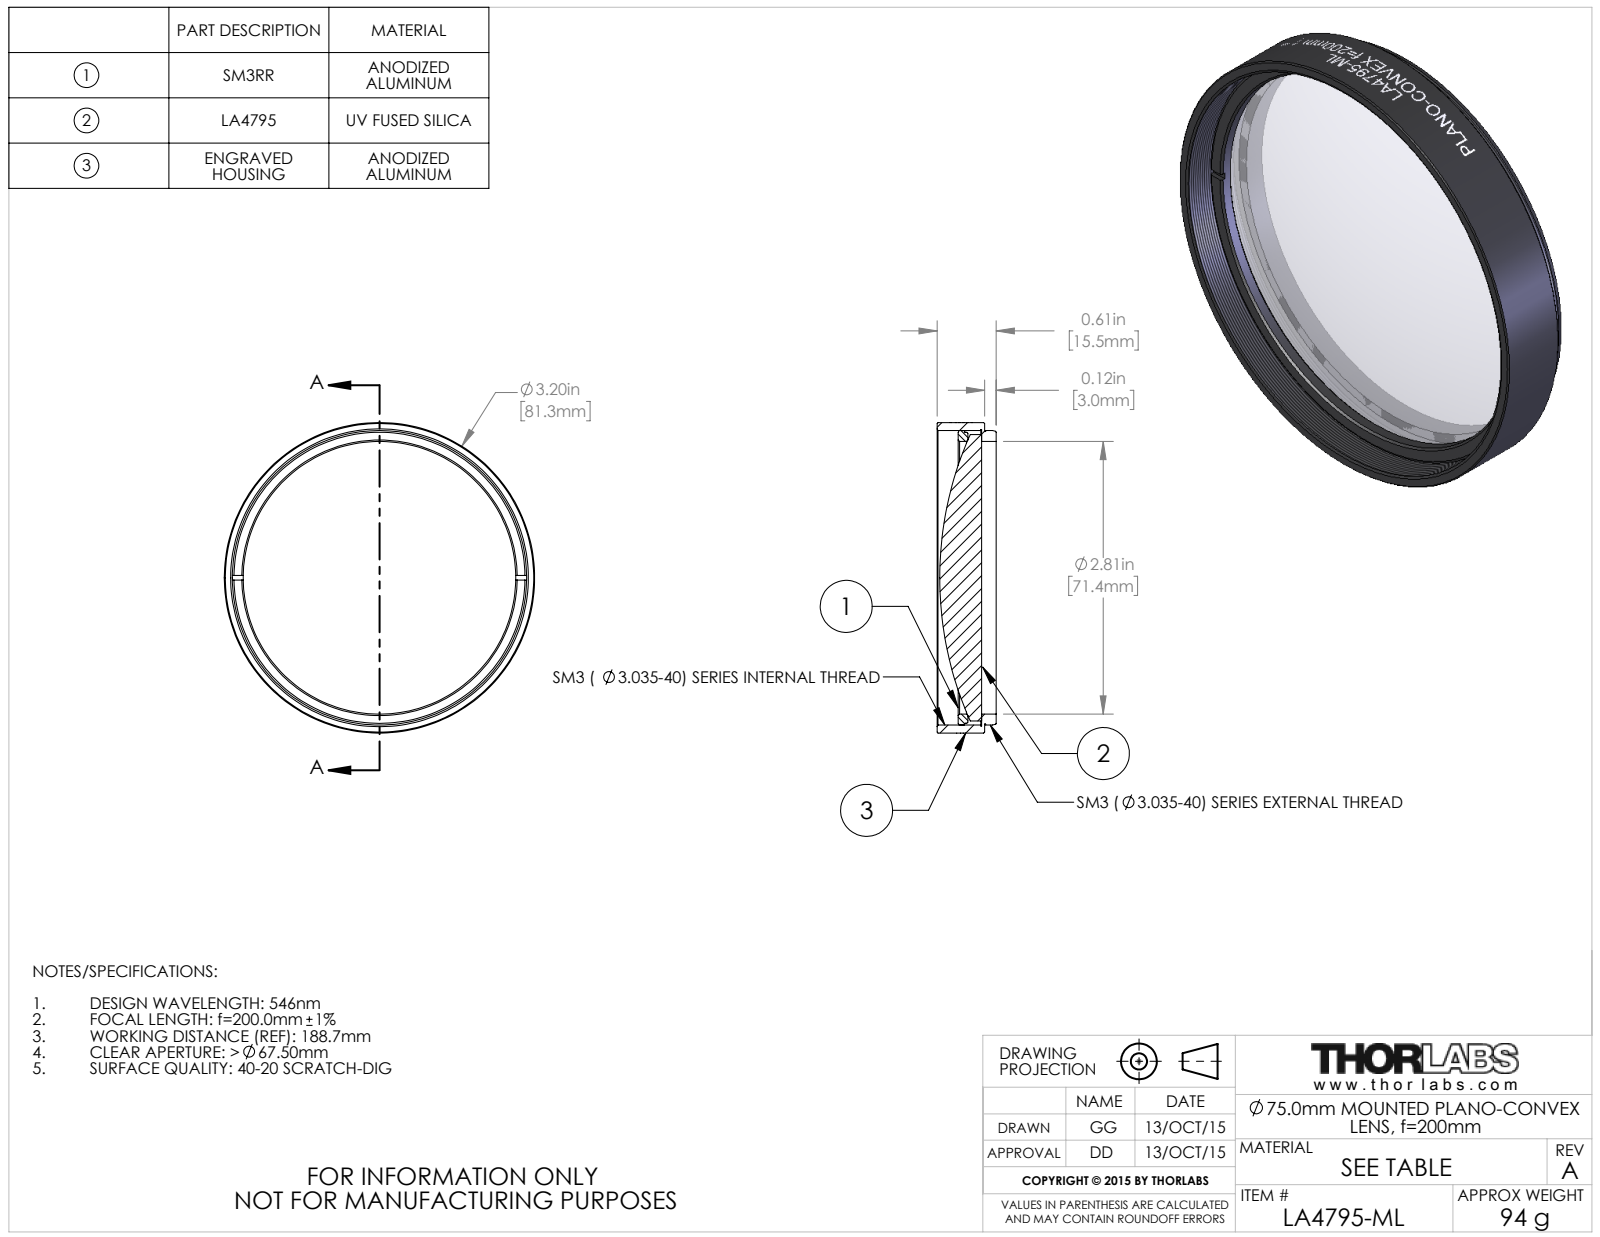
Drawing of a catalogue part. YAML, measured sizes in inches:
part_name: "TTN039398-E0W"
step_written_by: "SolidWorks 2016 (CONFIG_CONTROL_DESIGN)"
units: inches
bodies: {solids: 3, faces: 116, planar: 17, cylindrical: 75, other: 24}
overall_size: [3.2, 3.2, 0.61]
volume: 2.542
surface_area: 34.21
round_holes:
  - {diameter: 2.81, count: 1}
  - {diameter: 3.055, count: 1}
round_bosses_or_shafts:
  - {diameter: 3.2, count: 1}
  - {diameter: 3.035, count: 1}
  - {diameter: 3.015, count: 1}
  - {diameter: 2.998, count: 1}
  - {diameter: 2.953, count: 1}
face_to_face_distances: [0.15, 0.03, 0.12, 0.393, 0.273, 0.243, 0.173, 0.293, 0.143, 0.1]
